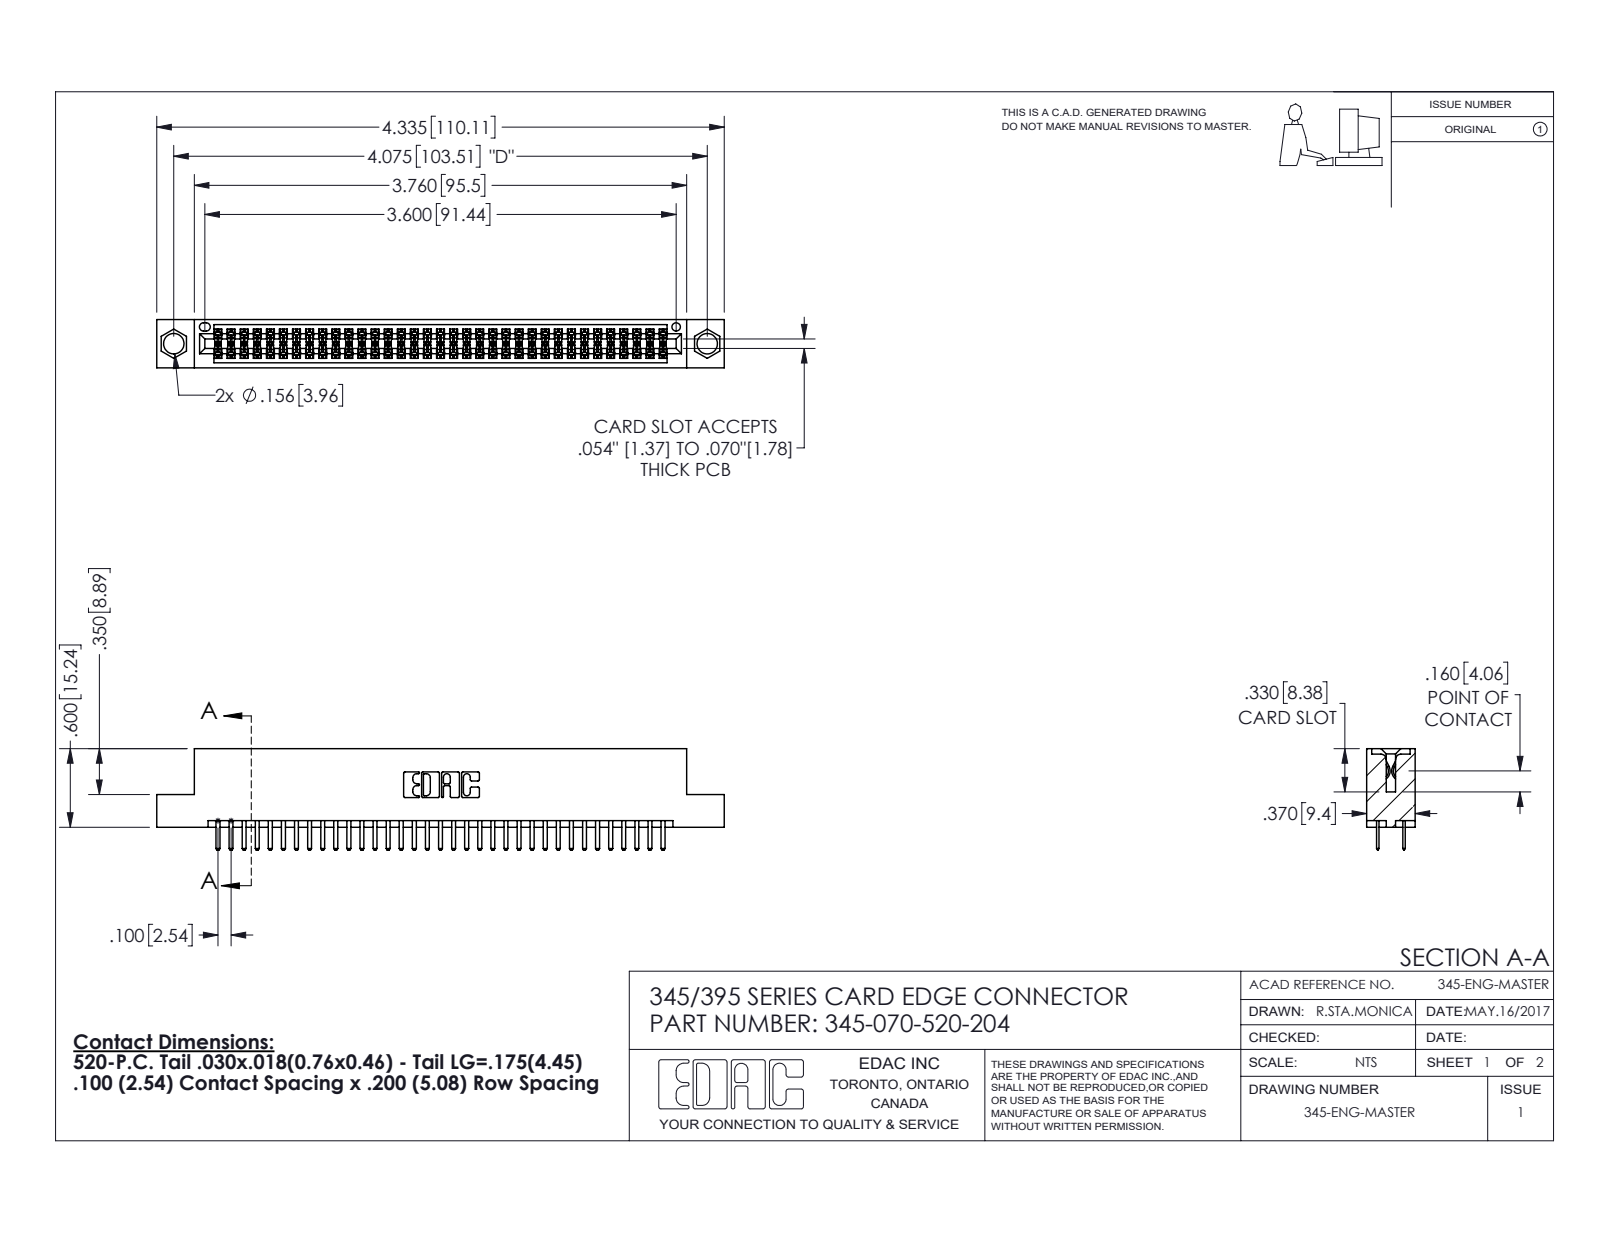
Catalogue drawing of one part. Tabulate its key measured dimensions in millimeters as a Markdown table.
| quantity | value |
| --- | --- |
| part name | 345-070-520-204; 345 Part_Flush Mounting Lugs - 0.156 Dia-TI; 345-292-001_345-293-120 |
| STEP written by | SolidWorks 2020 (CONFIG_CONTROL_DESIGN) |
| units | millimeters |
| bodies | 71 solids, 3920 faces (2544 planar, 1376 cylindrical, 0 other) |
| overall size | 110.1 × 19.7 × 9.4 |
| volume | 10 500 mm³ |
| surface area | 15 160 mm² |
| round holes (diameter × count) | 4 × 2, 1.6 × 1 |
| partial cylindrical surfaces (radius × count) | 0.2 × 105, 0.3 × 74, 0.3 × 22, 0.2 × 6, 0.8 × 6, 0.7 × 3, 0.4 × 2, 0.5 × 2 |
| main face-to-face distances | 7.6, 1.8, 5.1, 9.4, 2.5, 6.9, 0.6, 5.7, 0.6, 1.8 |
| hole center spacings | 6.9, 97.5, 103.5 |
